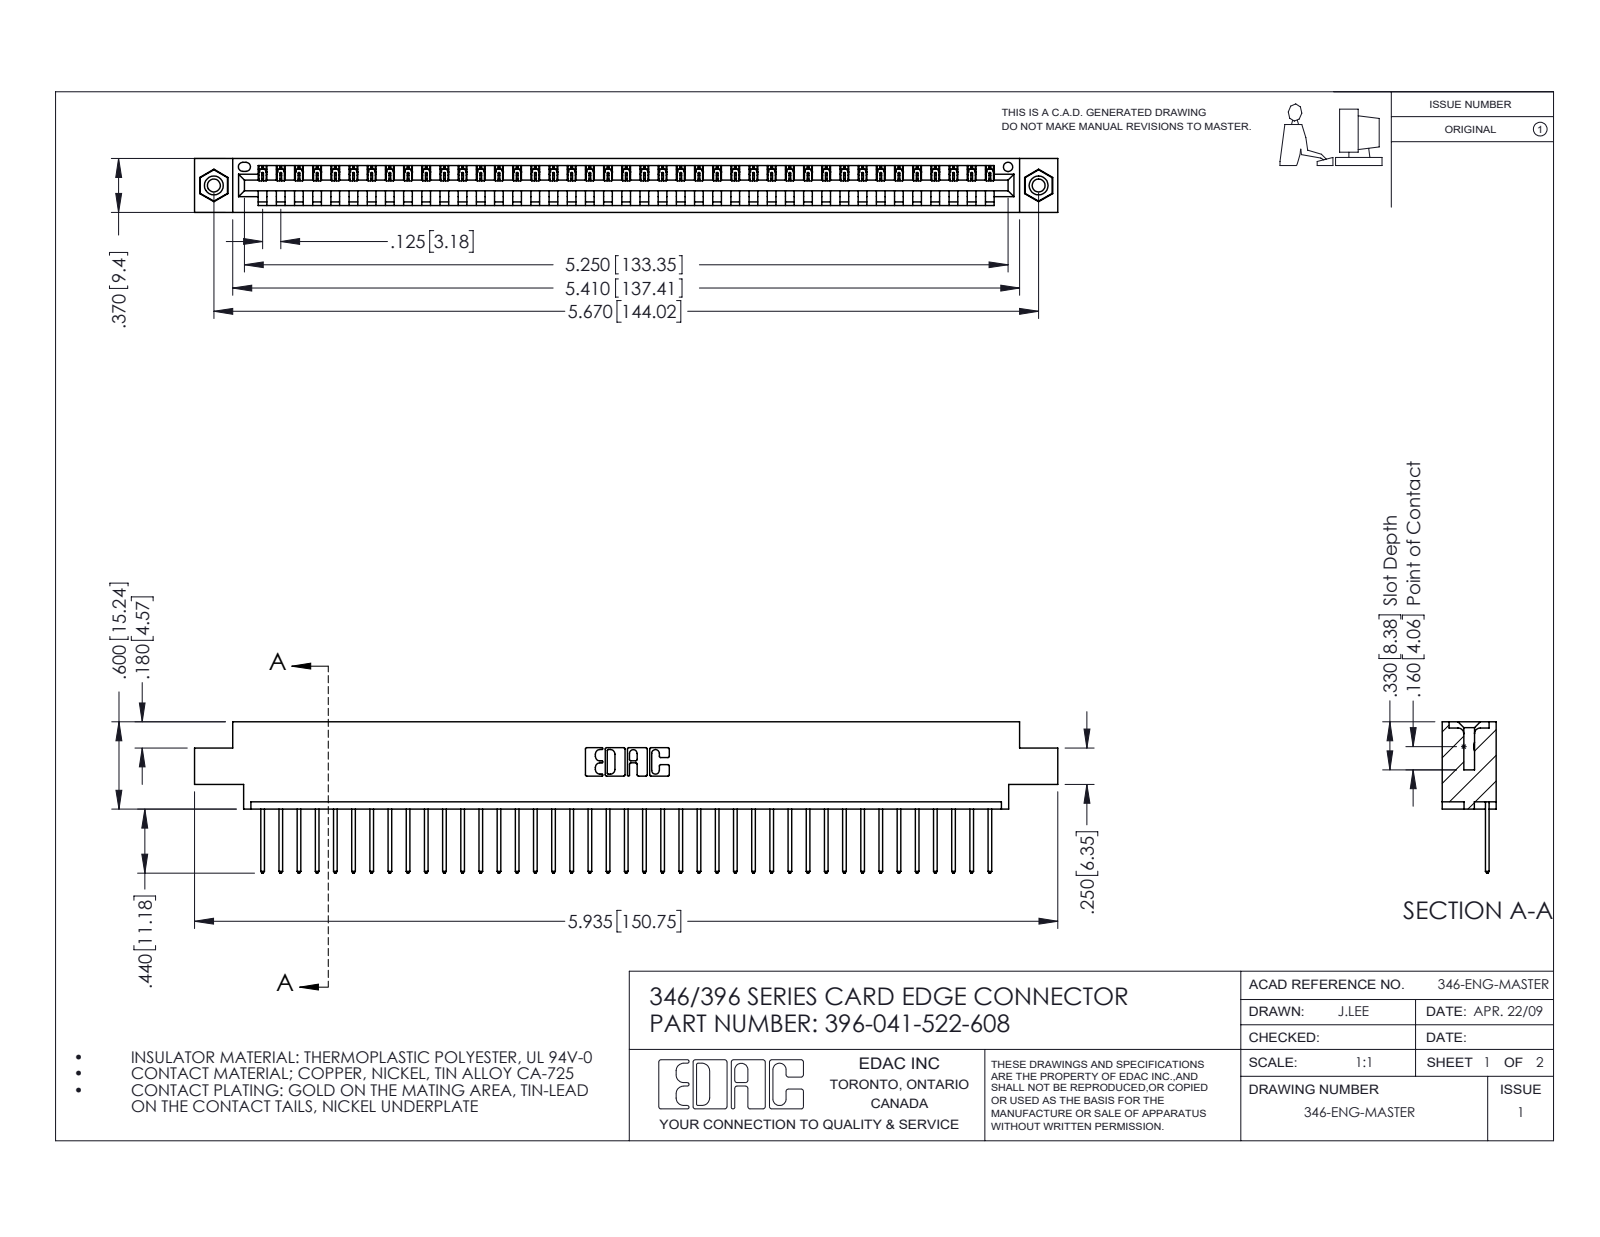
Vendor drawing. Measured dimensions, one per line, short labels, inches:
name: 345-292-001_345-293-122; 396-041-522-608; 346 Part_0.170 Offset - 0.156 Dia-TI; 345-250-001_345-250-003-102
written by: SolidWorks 2016 (CONFIG_CONTROL_DESIGN)
unit: in
bodies: 44 solids, 2564 faces (1752 planar, 796 cylindrical, 16 other)
size: 5.935 × 1.04 × 0.37
volume: 0.871 in³; area: 28.14 in²
holes: 2× ⌀0.089, 2× ⌀0.125, 2× ⌀0.156, 1× ⌀0.064
bosses: 2× ⌀0.155
rounds: 82× R0.006, 82× R0.01, 22× R0.01, 6× R0.007, 6× R0.031, 3× R0.026, 2× R0.031, 2× R0.04
face distances: 0.048, 0.322, 0.37, 0.25, 0.072, 0.298, 0.025, 0.222, 0.148, 0.1
hole spacings: 0.246, 5.461, 5.67
